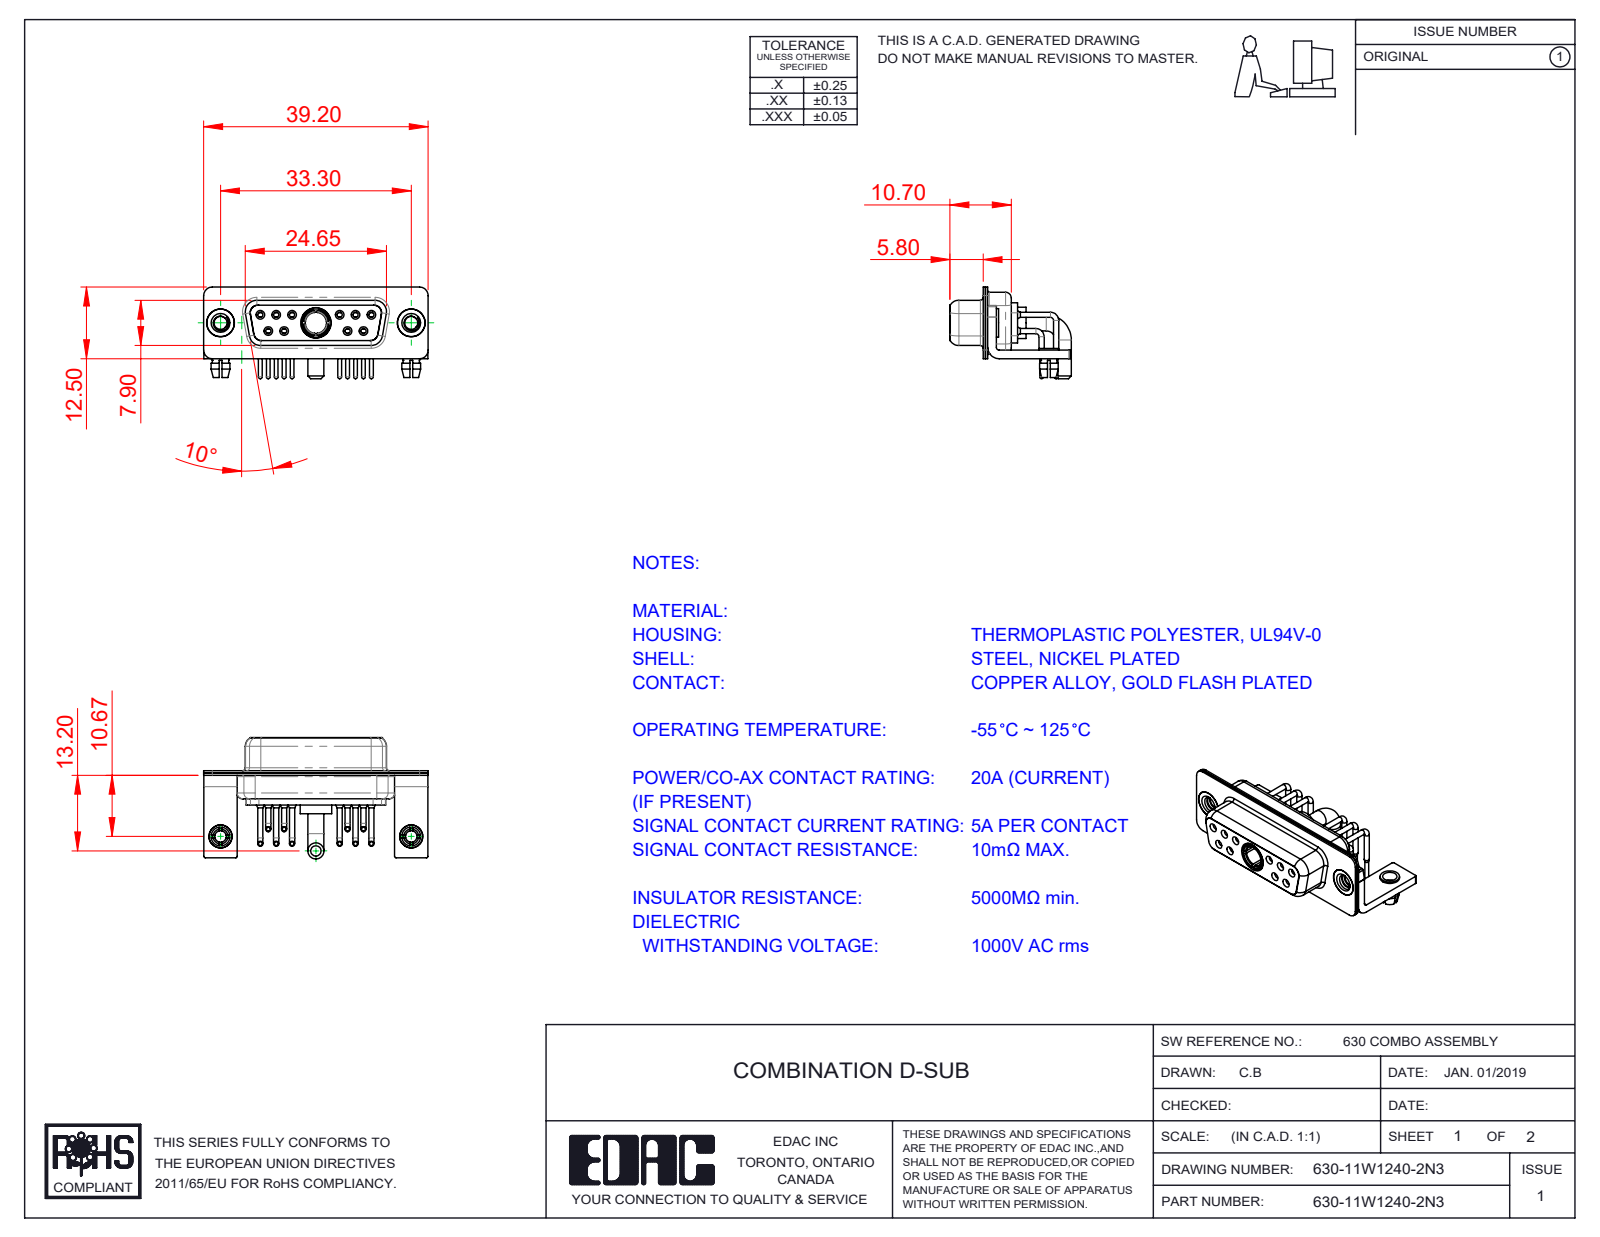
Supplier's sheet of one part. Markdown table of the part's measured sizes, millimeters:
| quantity | value |
| --- | --- |
| part name | 630Combo Contact Row 1; 630Combo Contact Row 2; Power Socket_20A RA; 630Combo Board Lock (+6 more) |
| STEP written by | SolidWorks 2020 (CONFIG_CONTROL_DESIGN) |
| units | millimeters |
| bodies | 21 solids, 1019 faces (314 planar, 442 cylindrical, 263 other) |
| overall size | 39.2 × 21.2 × 16 |
| volume | 2 950 mm³ |
| surface area | 7 069 mm² |
| round holes (diameter × count) | 2 × 12, 0.9 × 10, 1.1 × 10, 1.5 × 10, 1.7 × 6, 1.6 × 4, 4.85 × 3, 2.26 × 2, 2.5 × 2, 3.2 × 2, 4 × 2, 4.05 × 2 |
| round bosses / shafts (diameter × count) | 0.9 × 10, 0.65 × 10, 1.6 × 6, 5 × 2, 4.95 × 2, 4.8 × 2, 4 × 2, 3.4 × 2 |
| partial cylindrical surfaces (radius × count) | 0.25 × 16, 1.5 × 16, 2 × 13, 1.35 × 12, 1.6 × 8, 0.5 × 5, 0.6 × 4, 0.65 × 4 |
| main face-to-face distances | 0.4, 0.8, 0.45, 1.4, 8.45, 1.5, 1.8, 8.9, 6.2, 2.3 |
| hole center spacings | 3.16, 2.77, 13.85, 11.08, 16.62, 5.03, 5.04, 5.54 |
